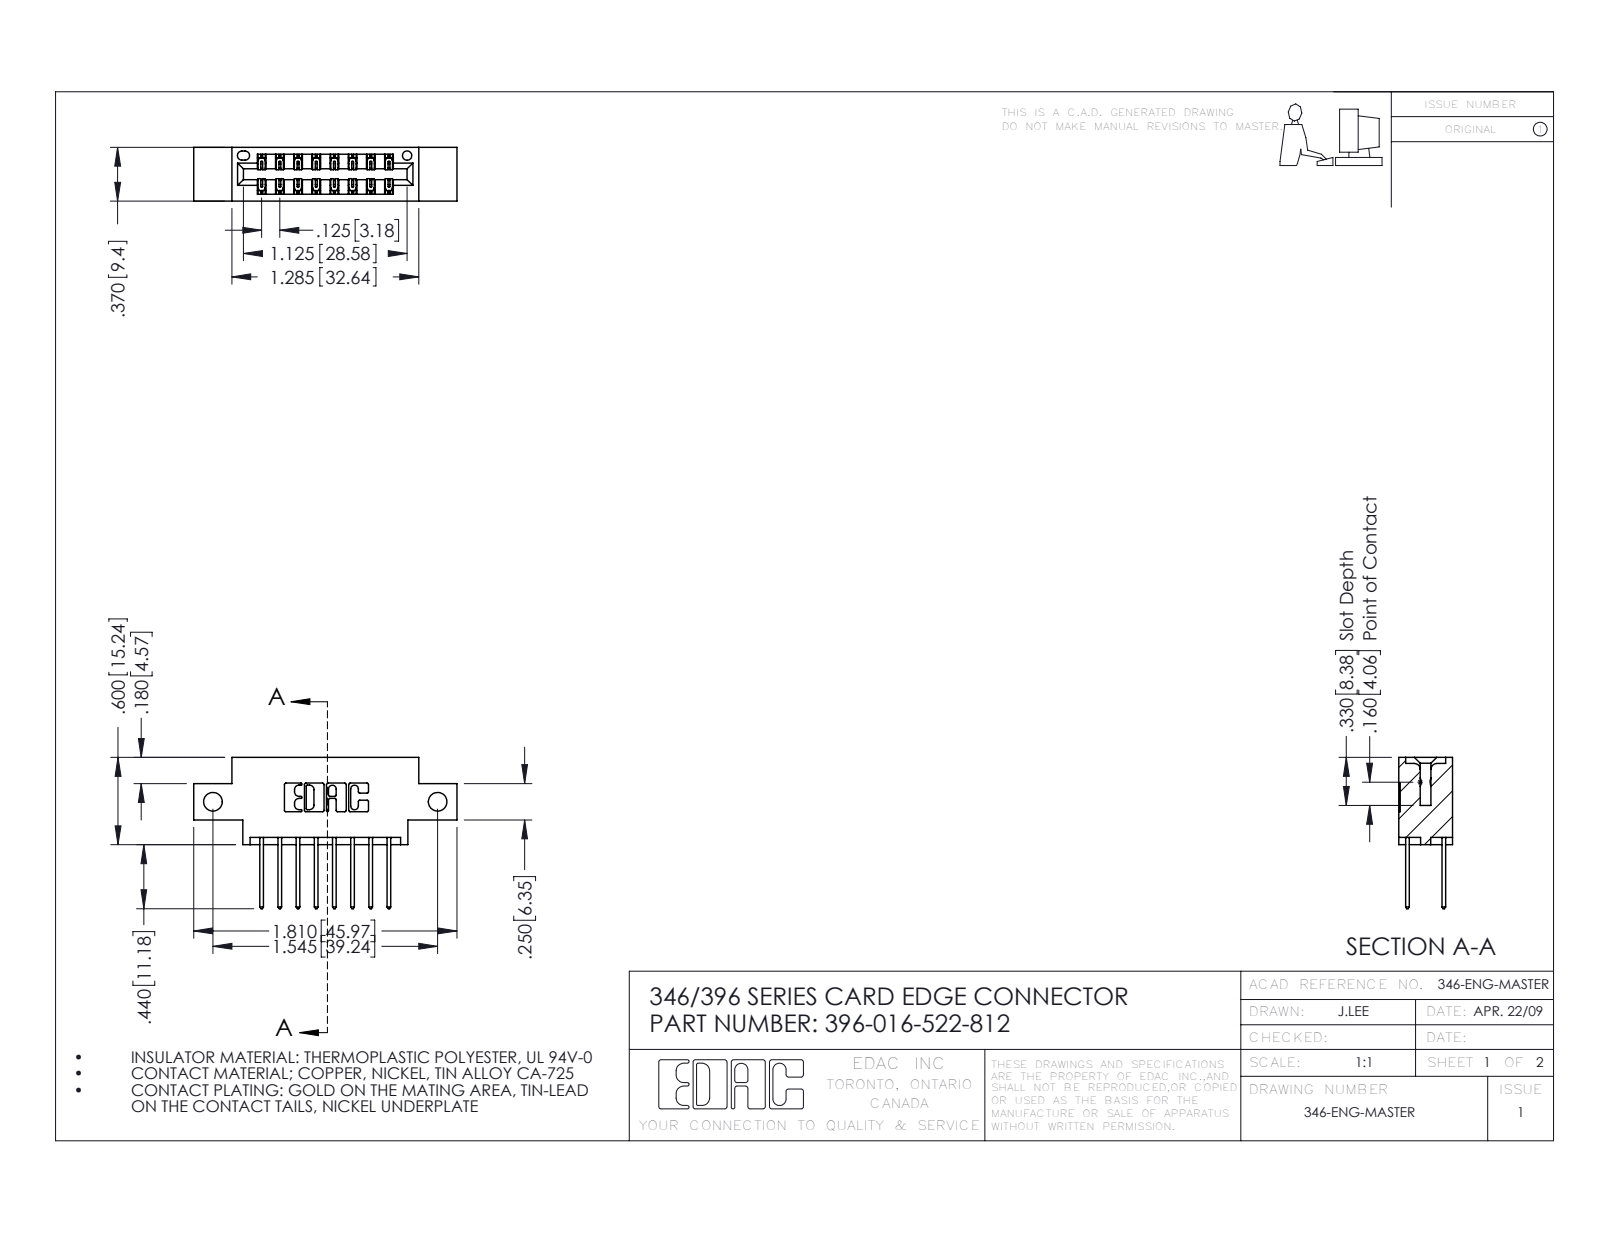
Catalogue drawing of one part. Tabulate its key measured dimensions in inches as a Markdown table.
| quantity | value |
| --- | --- |
| part name | 346 Part_0.170 Offset - Side Mount; 345-292-001_345-293-122; 396-016-522-812 |
| STEP written by | SolidWorks 2016 (CONFIG_CONTROL_DESIGN) |
| units | inches |
| bodies | 17 solids, 958 faces (640 planar, 318 cylindrical, 0 other) |
| overall size | 1.81 × 1.04 × 0.37 |
| volume | 0.245 in³ |
| surface area | 8.092 in² |
| round holes (diameter × count) | 0.128 × 2, 0.064 × 1 |
| partial cylindrical surfaces (radius × count) | 0.006 × 24, 0.01 × 22, 0.01 × 16, 0.007 × 6, 0.031 × 6, 0.026 × 3, 0.014 × 2, 0.022 × 2 |
| main face-to-face distances | 0.25, 0.048, 0.322, 0.37, 0.072, 0.298, 0.025, 0.275, 0.148, 0.222 |
| hole center spacings | 1.545 |
